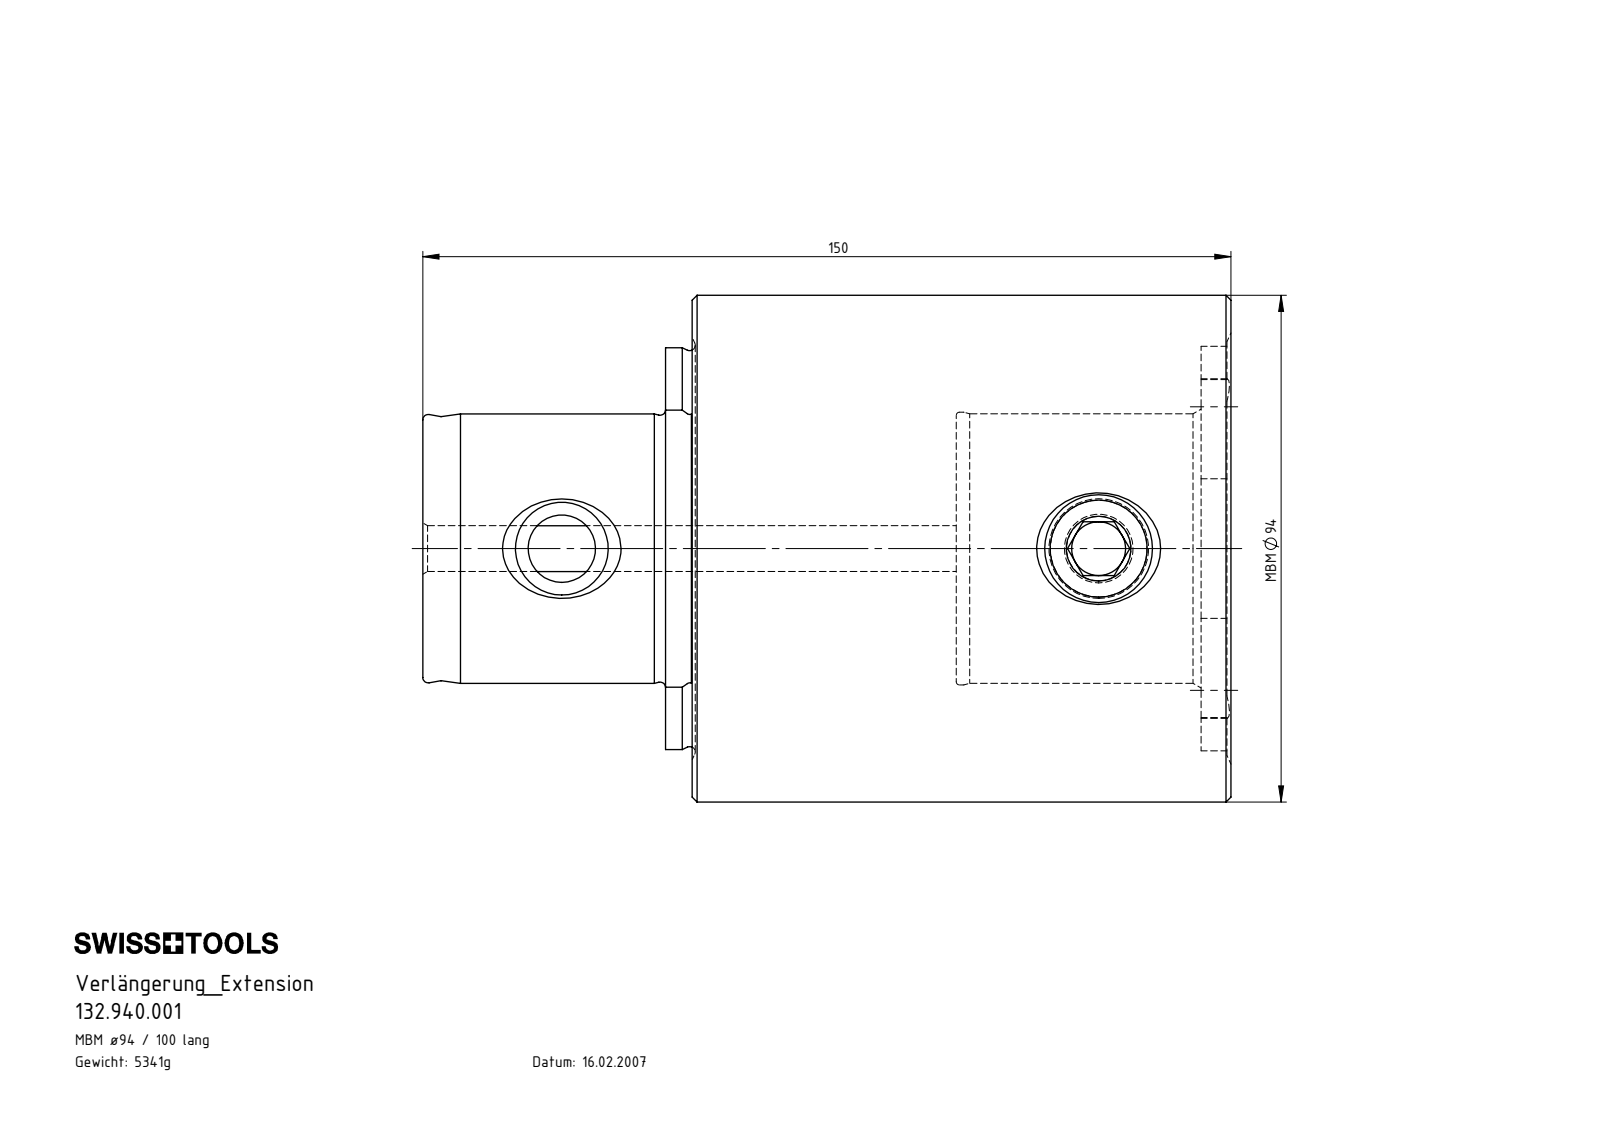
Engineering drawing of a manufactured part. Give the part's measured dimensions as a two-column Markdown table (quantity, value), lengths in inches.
| quantity | value |
| --- | --- |
| part name | MB9-MB9.K01.100_B; MB9-MB9.K01.100; MB9-ER1.001.032_A |
| STEP written by | SolidWorks 2017 (AUTOMOTIVE_DESIGN) |
| units | inches |
| bodies | 2 solids, 129 faces (34 planar, 34 cylindrical, 61 other) |
| overall size | 5.906 × 3.701 × 3.701 |
| volume | 41.52 in³ |
| surface area | 102.3 in² |
| round holes (diameter × count) | 0.335 × 1, 0.394 × 1, 0.492 × 1, 0.728 × 1, 1.969 × 1, 1.992 × 1 |
| round bosses / shafts (diameter × count) | 3.701 × 1, 0.787 × 1 |
| partial cylindrical surfaces (radius × count) | 0.205 × 4, 1.181 × 1, 1.467 × 1, 1.477 × 1 |
| main face-to-face distances | 3.913, 1.929, 1.969, 3.898, 5.687, 3.719, 1.789, 5.906, 3.937, 2.008 |
| hole center spacings | 3.923 |
